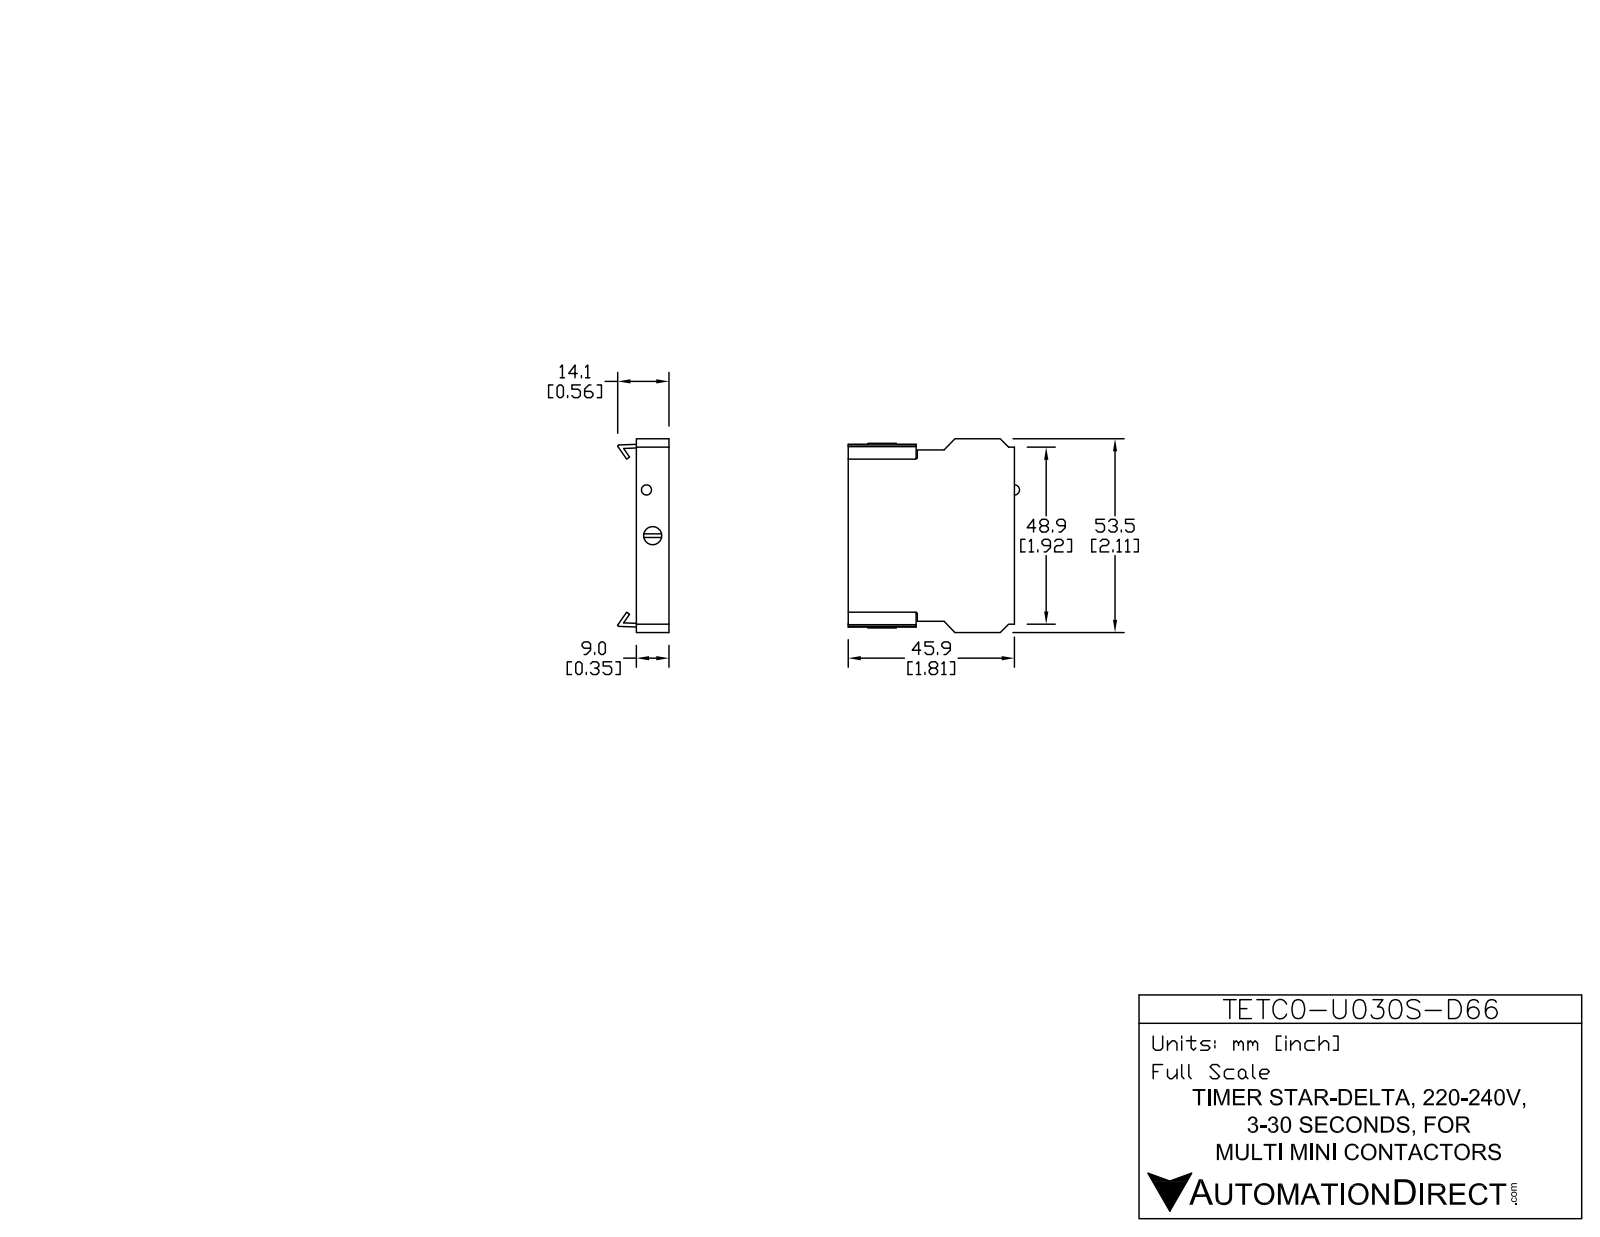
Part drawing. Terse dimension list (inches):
name: TETC0-U030S-D66
written by: SolidWorks 2013 (AUTOMOTIVE_DESIGN)
unit: in
bodies: 3 solids, 102 faces (76 planar, 22 cylindrical, 4 other)
size: 2.106 × 1.886 × 0.533
volume: 1.365 in³; area: 11.58 in²
holes: 1× ⌀0.022, 1× ⌀0.118, 1× ⌀0.217
bosses: 1× ⌀0.207
rounds: 2× R0.012, 2× R0.031, 2× R0.039, 2× R0.079
face distances: 0.394, 1.807, 0.039, 0.209, 1.897, 0.122, 1.984, 0.087, 1.775, 1.687
hole spacings: 0.073, 0.483, 0.554
